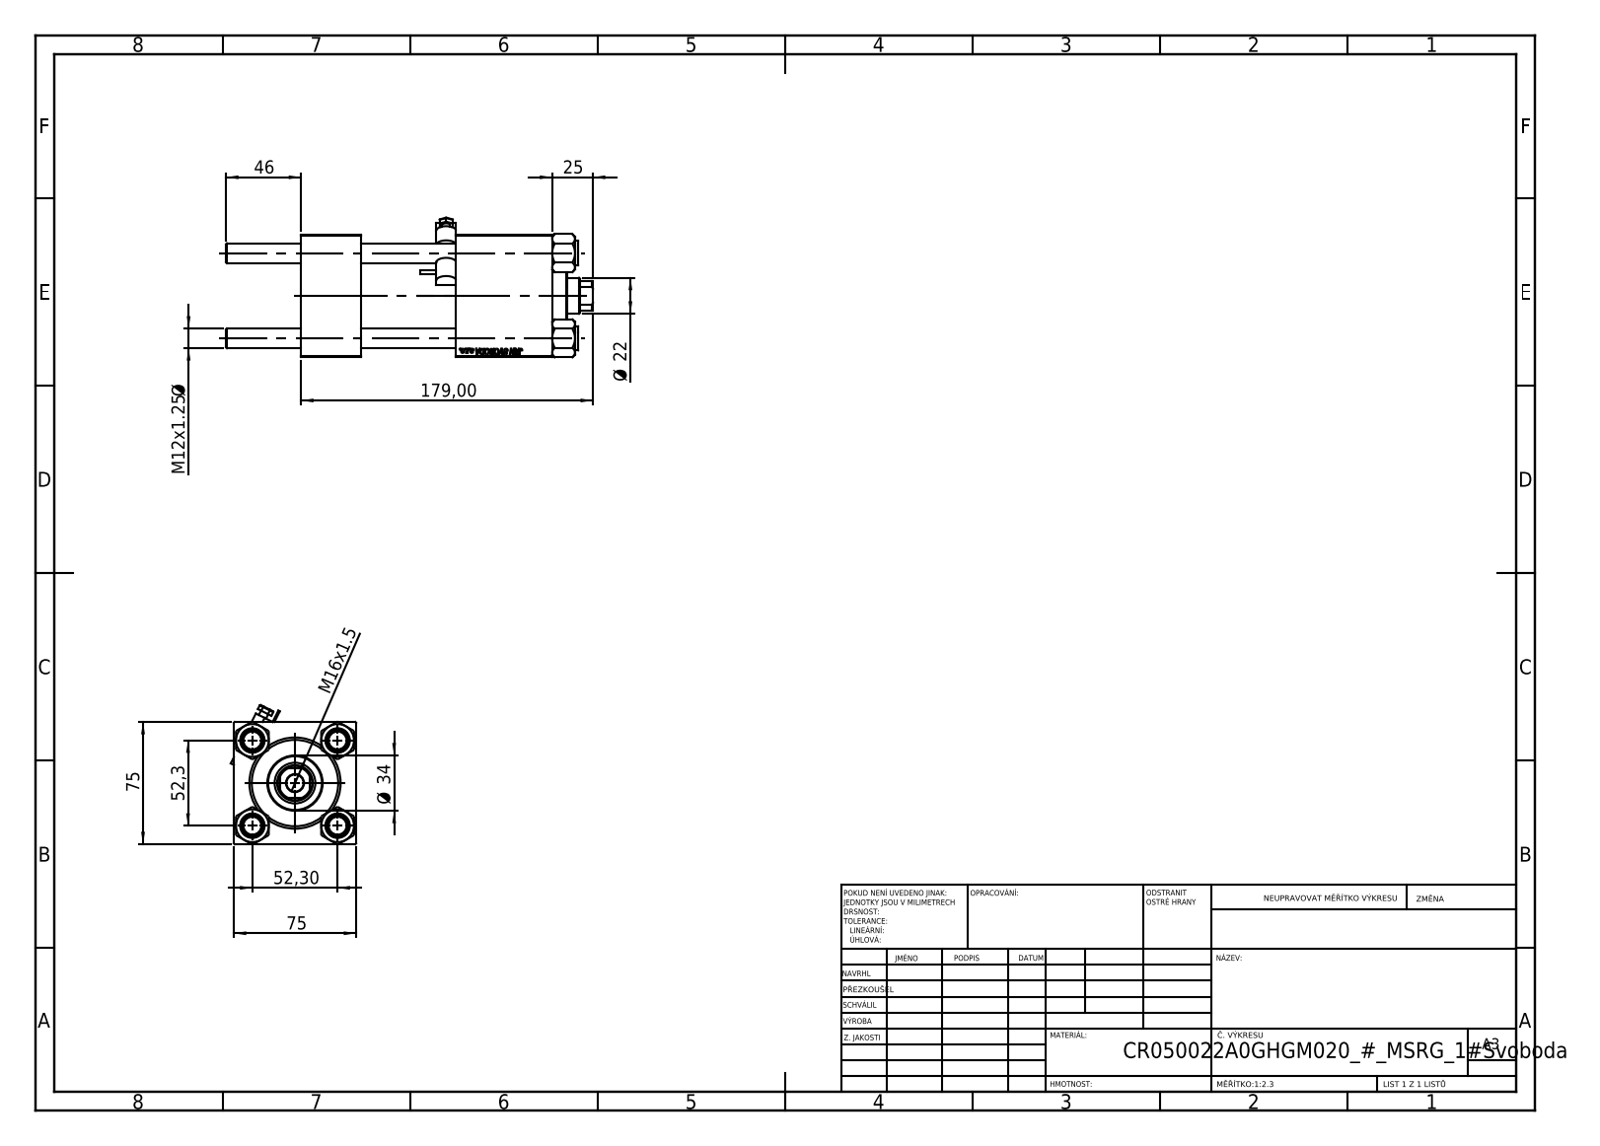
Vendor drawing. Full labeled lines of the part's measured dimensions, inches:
Part name (STEP PRODUCT): CR025_012_A_0_G_A_G_M_020_+#_##_TYCINKA; NUT_M5; V215CR_BODY_A; V215CR_VCP (+2 more)
STEP written by: SolidWorks 2019 (CONFIG_CONTROL_DESIGN)
Units: inches
Bodies: 12 solids, 1166 faces (538 planar, 92 cylindrical, 536 other)
Overall size (bounding box): 8.858 × 3.373 × 3.027
Volume: 42.34 in³ · Surface area: 257.3 in²
Round holes (diameter × count): ⌀0.472 ×4, ⌀0.276 ×2, ⌀0.825 ×2, ⌀1.181 ×2, ⌀0.413 ×1, ⌀0.866 ×1, ⌀0.984 ×1, ⌀1.614 ×1, ⌀1.969 ×1, ⌀2.087 ×1
Round bosses / shafts (diameter × count): ⌀0.591 ×4, ⌀2.205 ×1, ⌀1.339 ×1, ⌀0.197 ×1, ⌀0.098 ×1
Partial cylindrical surfaces — rounded edges, fillets, slot ends (radius × count): R0.02 ×6, R0.236 ×2, R0.413 ×1
Main face-to-face distances: 2.953, 1.457, 6.063, 4.606, 3.74, 2.283, 2.323, 4.933, 3.476, 1.193
Hole centre spacings: 1.456, 2.059, 2.912, 3.681
